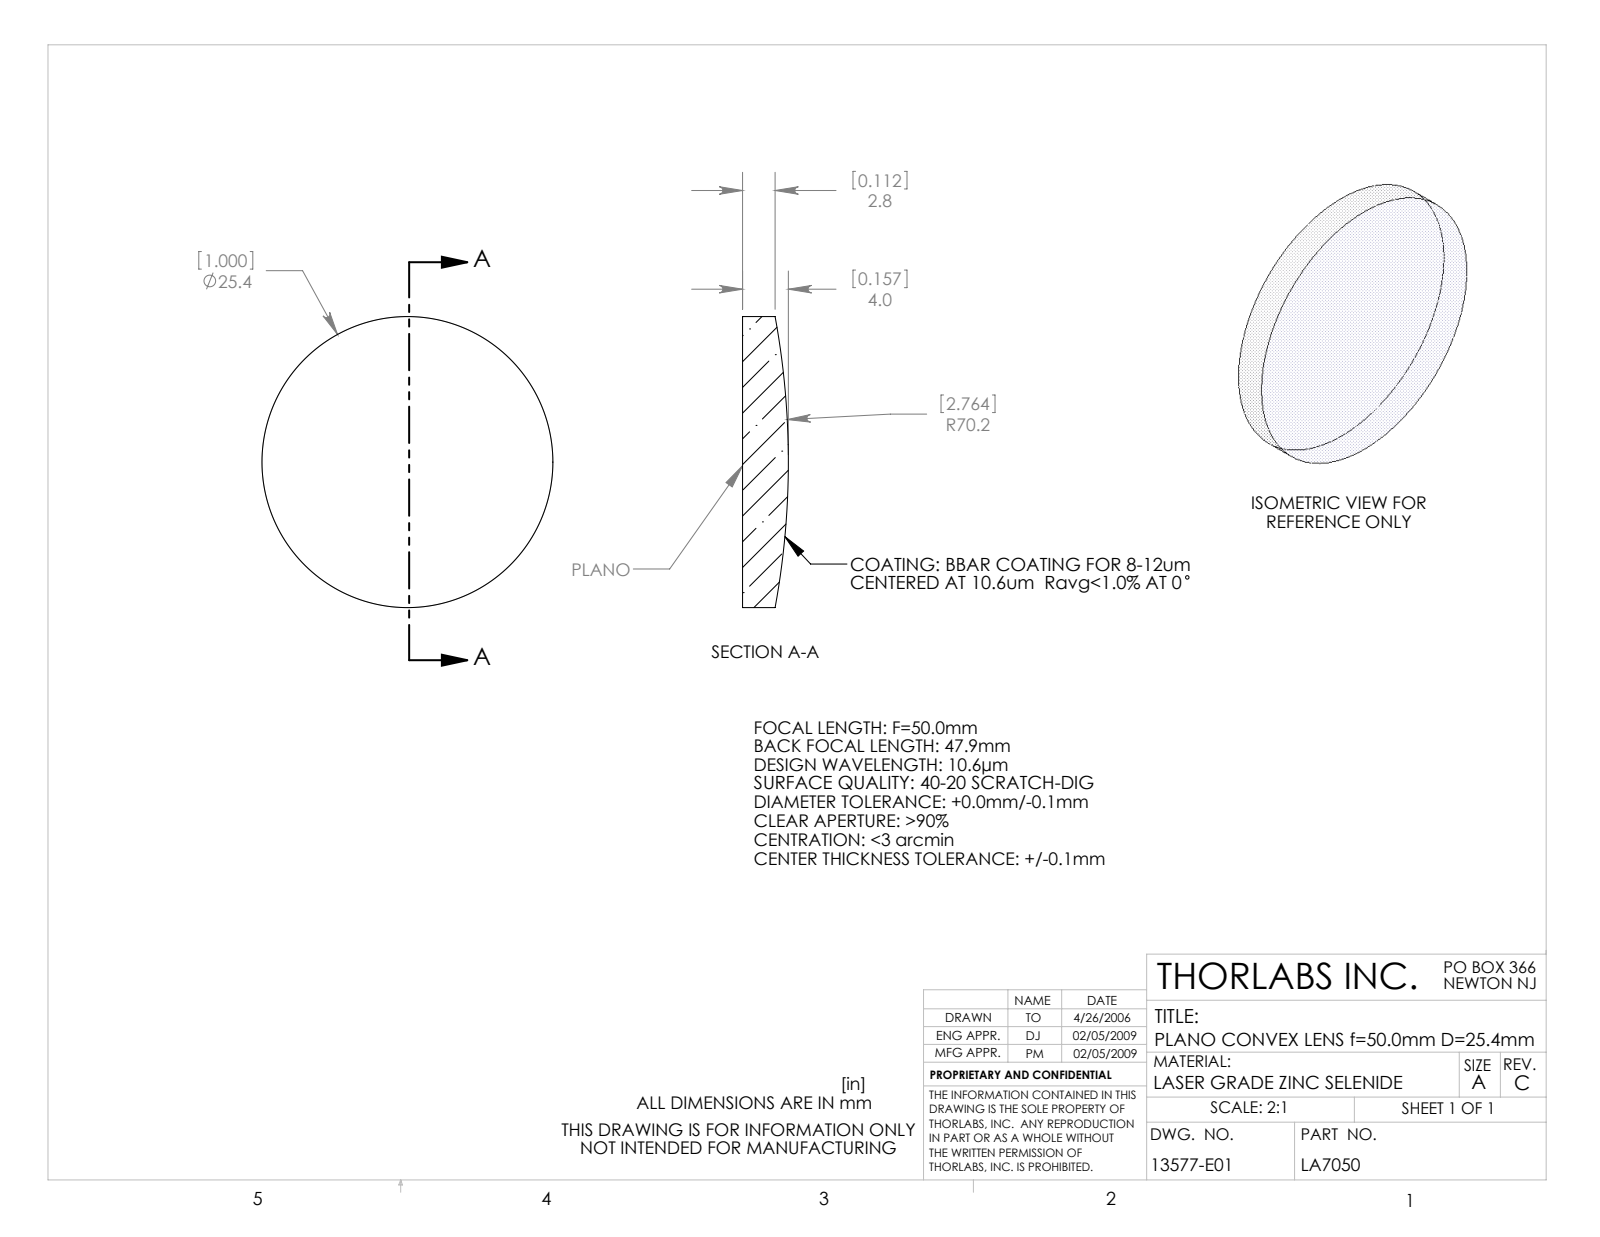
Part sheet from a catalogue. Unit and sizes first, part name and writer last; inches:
Units: inches
Overall size (bounding box): 1 × 1 × 0.157
Round bosses / shafts (diameter × count): ⌀1 ×1
Bodies: 0 solids, 5 faces (1 planar, 2 cylindrical, 2 other)
Part name (STEP PRODUCT): 13577-E0W
STEP written by: SolidWorks 2007 (AUTOMOTIVE_DESIGN)
